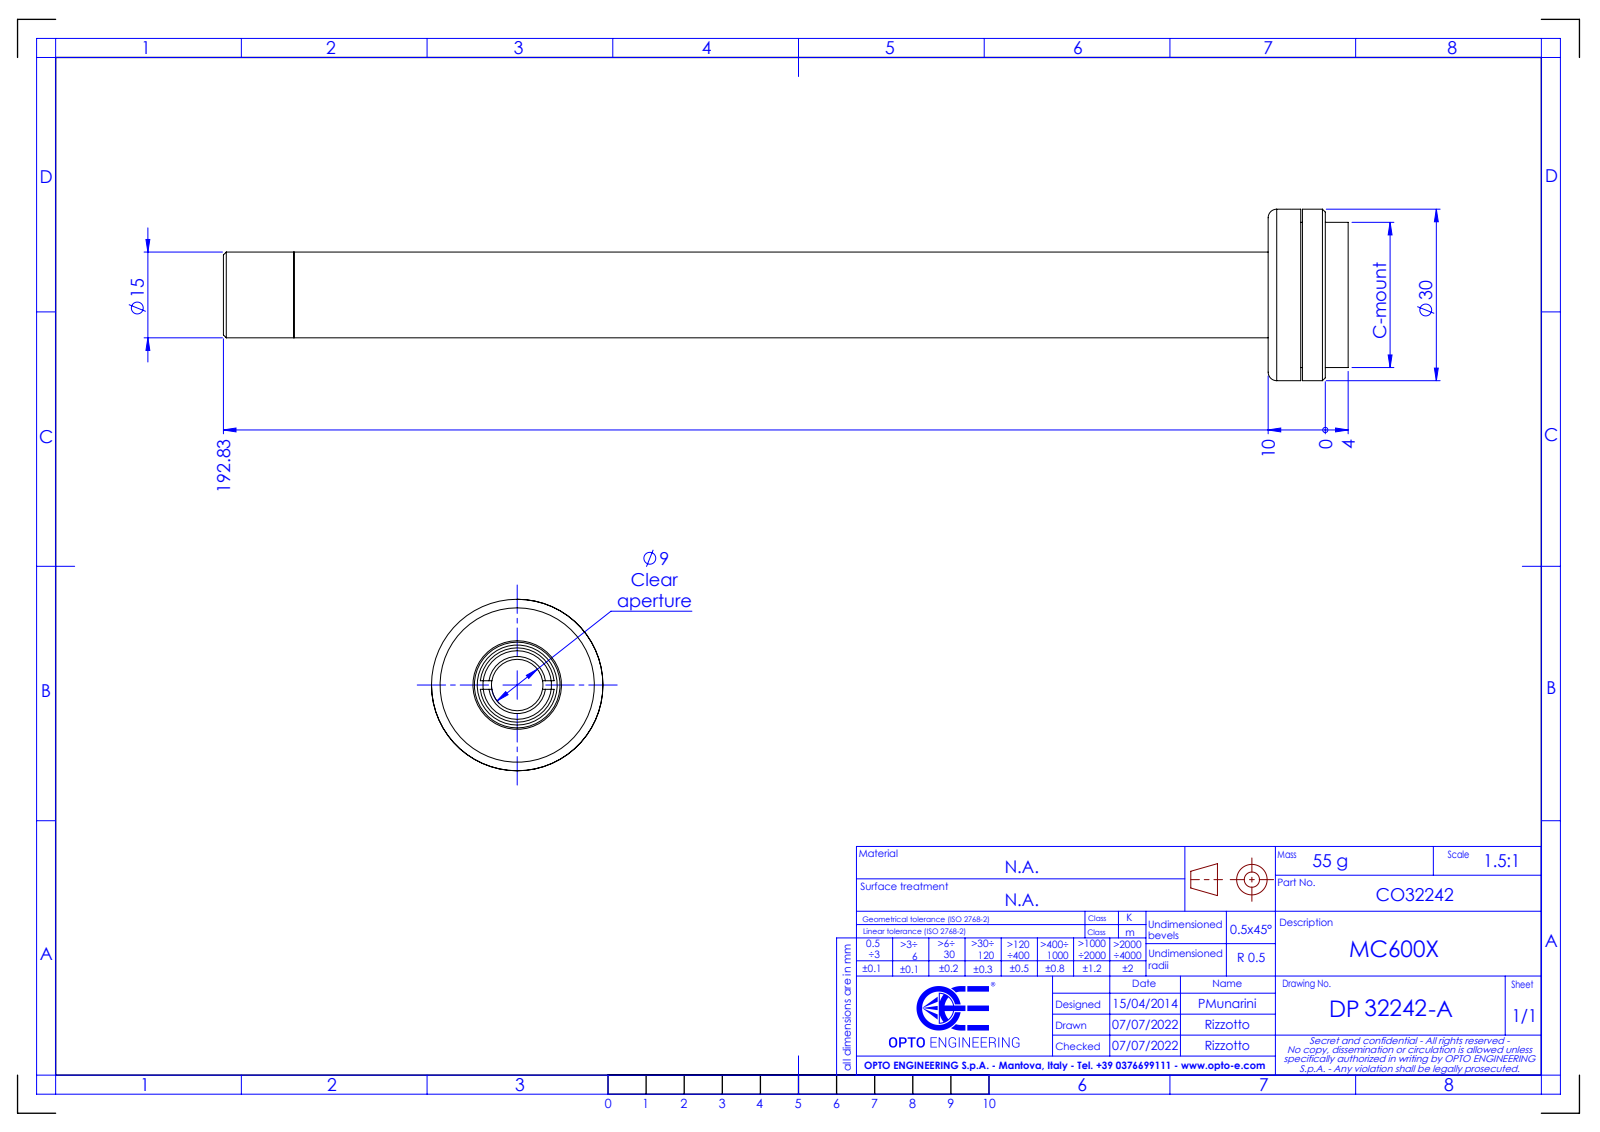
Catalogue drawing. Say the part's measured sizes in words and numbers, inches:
The part is named "DP32242-A_MC600X". Its 3-D file was written by "SolidWorks 2021 (CONFIG_CONTROL_DESIGN)". It is 0 solids with 47 faces: 14 planar, 18 cylindrical and 15 other. Overall it measures 7.749 by 1.181 by 1.181 inches. Round holes: 1 of diameter 0.354, 1 of diameter 0.472. Round bosses or shafts: 1 of diameter 1.181, 1 of diameter 1, 1 of diameter 0.591, 1 of diameter 0.571. The main face-to-face distances are 0.157, 0.236, 0.224, 0.394, 0.169, 0.551, 0.327, 0.315, 7.198, 7.422.
